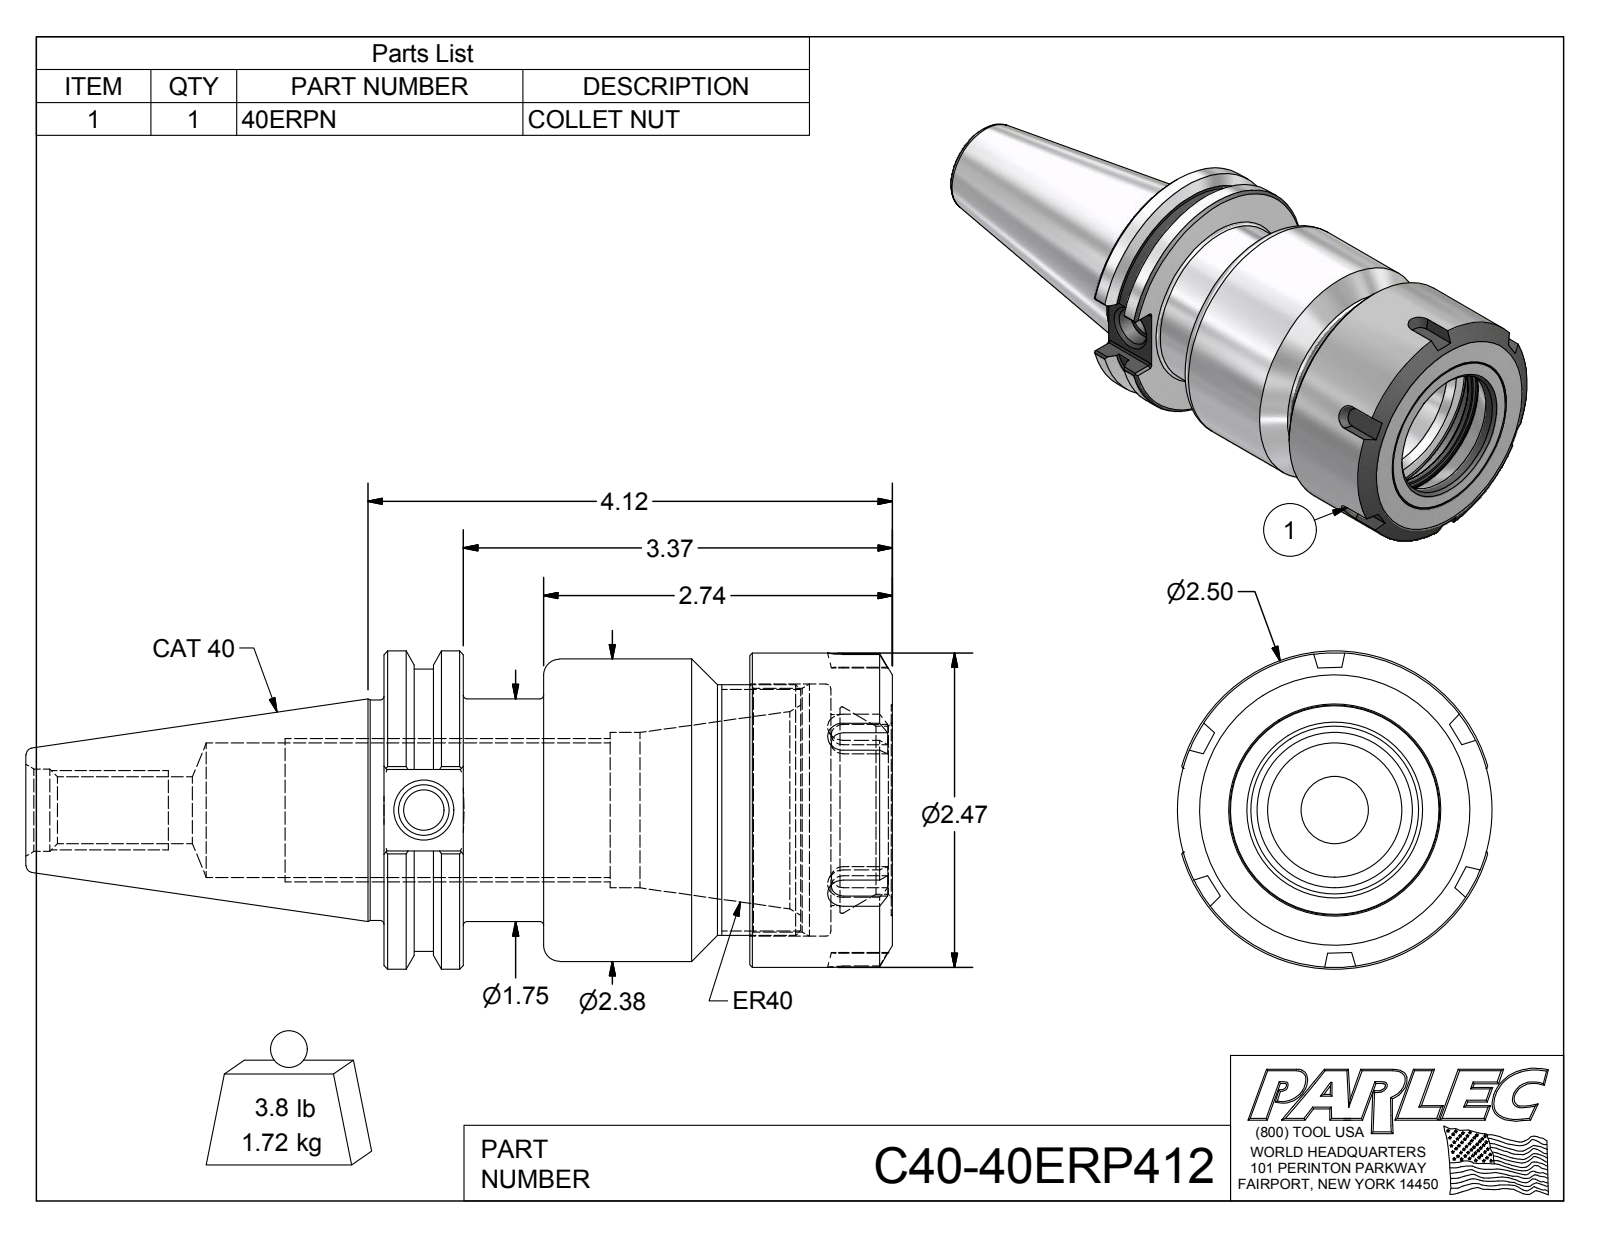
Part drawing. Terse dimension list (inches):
name: C40-40ERP412; C40-40ER4-1; 40ERPN
written by: Autodesk Inventor 2012 (AUTOMOTIVE_DESIGN)
unit: in
bodies: 2 solids, 133 faces (56 planar, 34 cylindrical, 43 other)
size: 6.808 × 2.5 × 2.47
volume: 13.48 in³; area: 85.42 in²
holes: 1× ⌀0.315, 1× ⌀0.399, 1× ⌀0.527, 1× ⌀0.648, 1× ⌀1.057, 1× ⌀1.22, 1× ⌀1.318, 1× ⌀1.5, 1× ⌀1.62, 1× ⌀1.916, 1× ⌀1.98
bosses: 1× ⌀2.5, 1× ⌀2.47, 1× ⌀2.375, 1× ⌀2.219, 1× ⌀1.969, 1× ⌀1.75, 1× ⌀1.73
rounds: 12× R0.02
face distances: 3.995, 0.625, 3.37, 2.875, 2.25, 1.12, 3.511, 2.886, 0.636, 0.484
